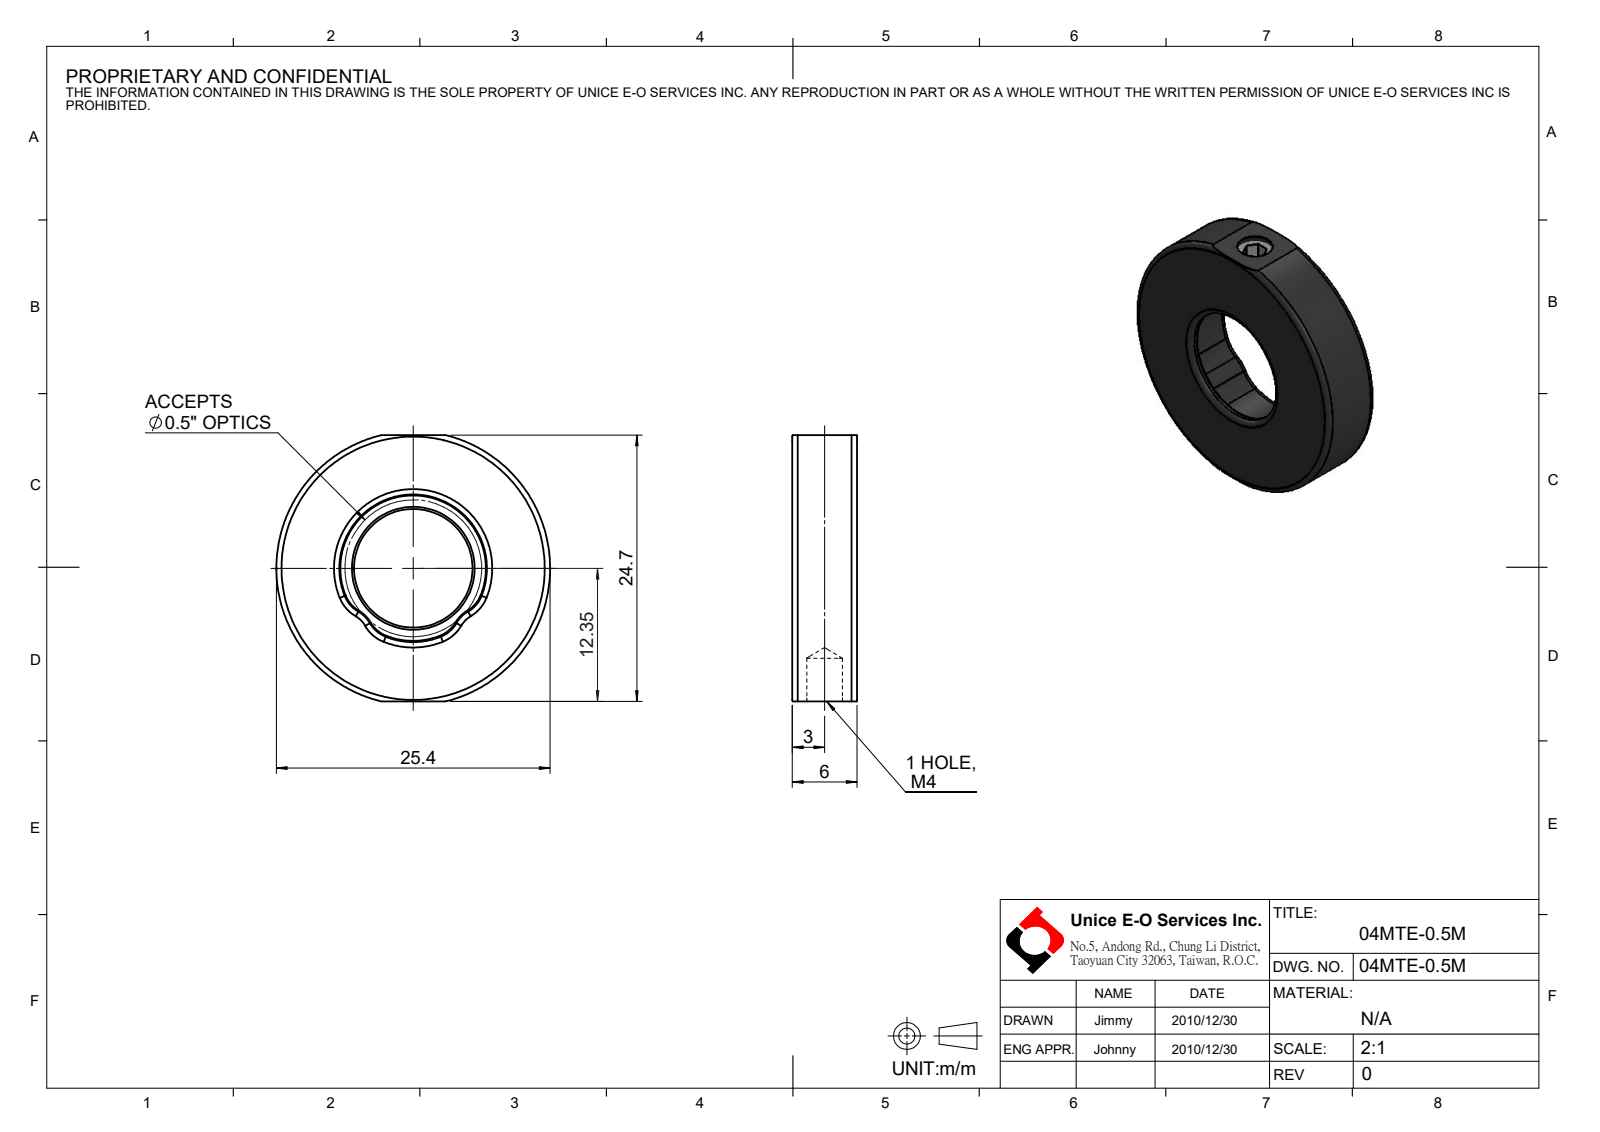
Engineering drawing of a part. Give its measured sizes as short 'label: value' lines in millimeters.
name: 04MTE-0.5M
written by: SolidWorks 2016 (CONFIG_CONTROL_DESIGN)
unit: mm
bodies: 3 solids, 77 faces (16 planar, 25 cylindrical, 36 other)
size: 25.4 × 24.7 × 6
volume: 2 151 mm³; area: 1 685 mm²
holes: 1× ⌀1.5, 1× ⌀3.3, 1× ⌀11
bosses: 1× ⌀25.4, 1× ⌀4, 1× ⌀1.6
rounds: 6× R3, 1× R6.85
face distances: 6, 1, 5, 24.7, 2, 4, 24.2, 0.5, 20.2, 4.5
